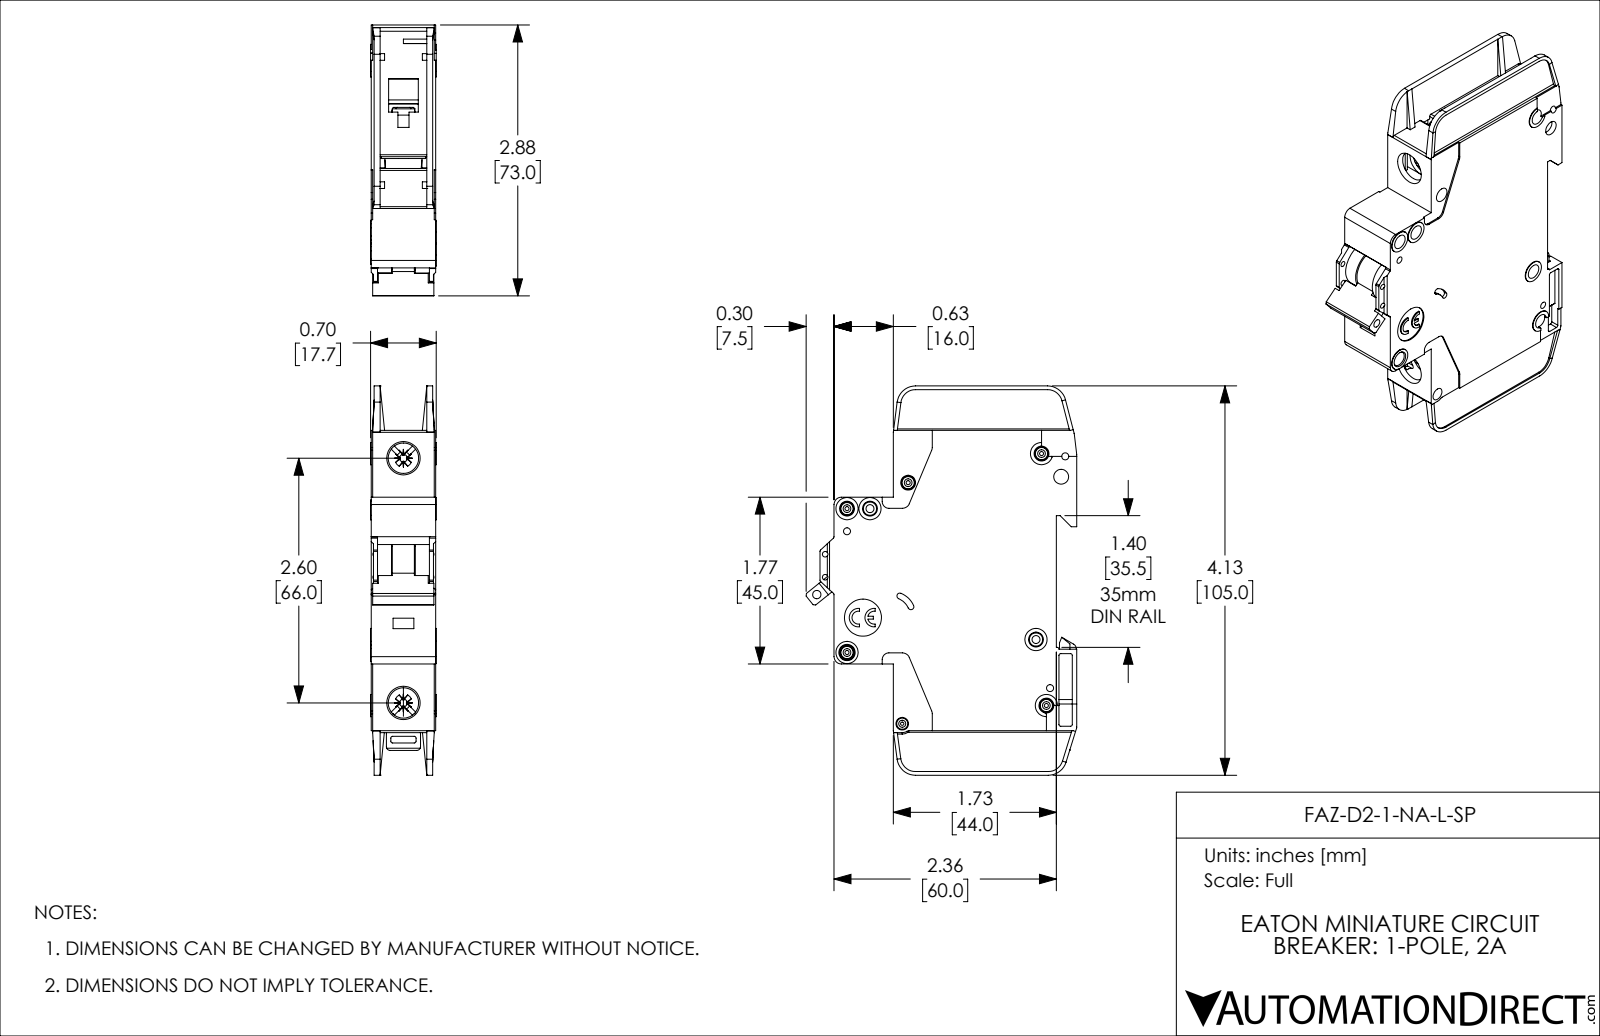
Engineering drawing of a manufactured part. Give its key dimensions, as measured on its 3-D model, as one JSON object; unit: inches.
{"part_name": "FAZ-D2-1-NA-L-SP", "step_written_by": "SolidWorks 2019 (AUTOMOTIVE_DESIGN)", "units": "inches", "bodies": {"solids": 1, "faces": 1127, "planar": 671, "cylindrical": 357, "other": 99}, "overall_size": [4.134, 2.876, 0.697], "volume_in3": 4.682, "surface_area_in2": 41.01, "round_holes": [[0.157, 8], [0.043, 5], [0.075, 4], [0.059, 2], [0.085, 2], [0.323, 2], [0.035, 1], [0.089, 1], [0.098, 1], [0.134, 1], [0.394, 1]], "round_bosses_or_shafts": [[0.13, 5], [0.236, 4], [0.118, 2], [0.098, 1]], "partial_cylinders_radius": [[0.02, 42], [0.016, 10], [0.039, 10], [0.079, 8], [0.197, 5], [0.008, 4], [0.026, 4], [0.043, 4]], "face_to_face_distances": [0.047, 0.685, 0.591, 0.638, 0.094, 0.543, 0.016, 0.031, 0.496, 0.575], "hole_center_spacings": [0.244, 0.537, 0.87, 0.189, 0.199, 0.204, 0.221, 0.24]}
